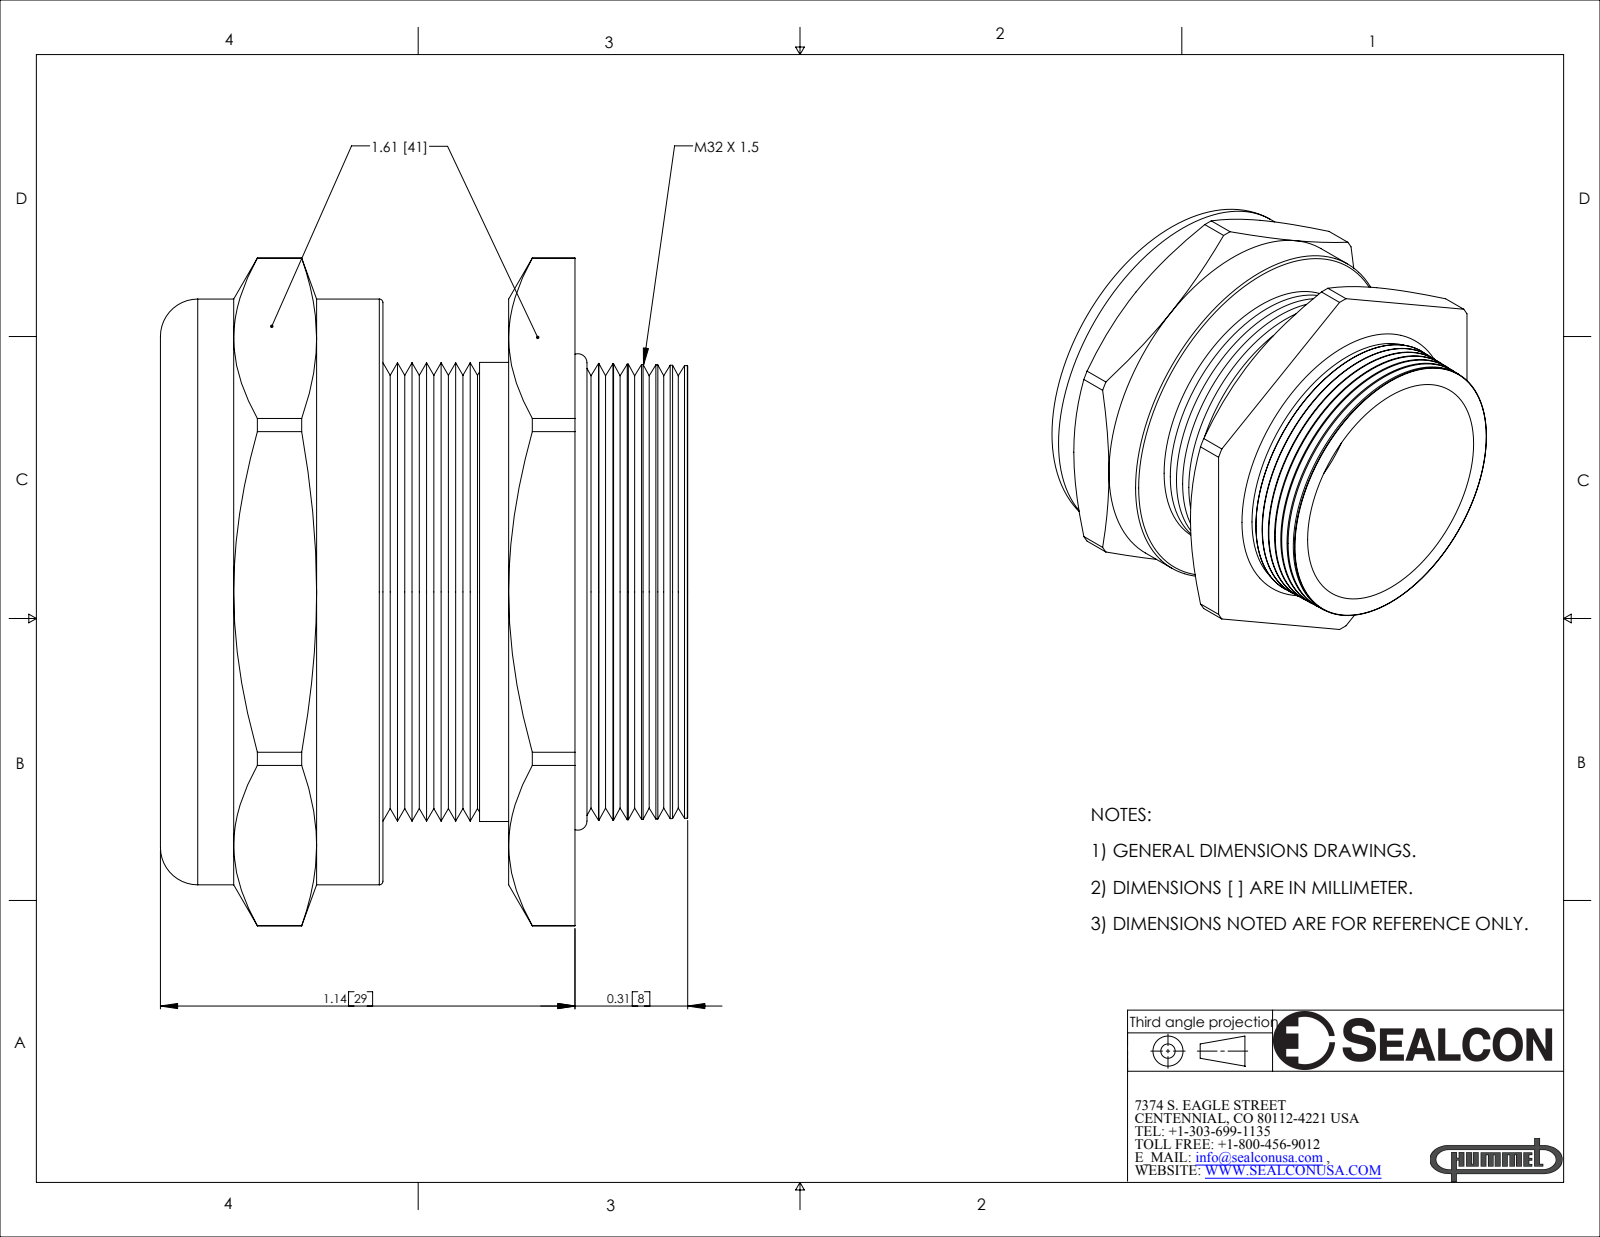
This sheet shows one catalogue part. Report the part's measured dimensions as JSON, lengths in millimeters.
{"part_name": "CD32MA-SS", "step_written_by": "SolidWorks 2007 (CONFIG_CONTROL_DESIGN)", "units": "millimeters", "bodies": {"solids": 2, "faces": 152, "planar": 22, "cylindrical": 28, "other": 102}, "overall_size": [46.6, 40.9, 36.8], "volume_mm3": 20840, "surface_area_mm2": 12820, "round_holes": [[25.4, 1], [29.6, 1], [32, 1]], "round_bosses_or_shafts": [[40.9, 1], [32.1, 1]], "partial_cylinders_radius": [[23.3, 1]], "face_to_face_distances": [40.9, 4.6, 8.8, 13.4, 10.4, 19.2, 23.9, 5.1, 15.5, 24.3]}
